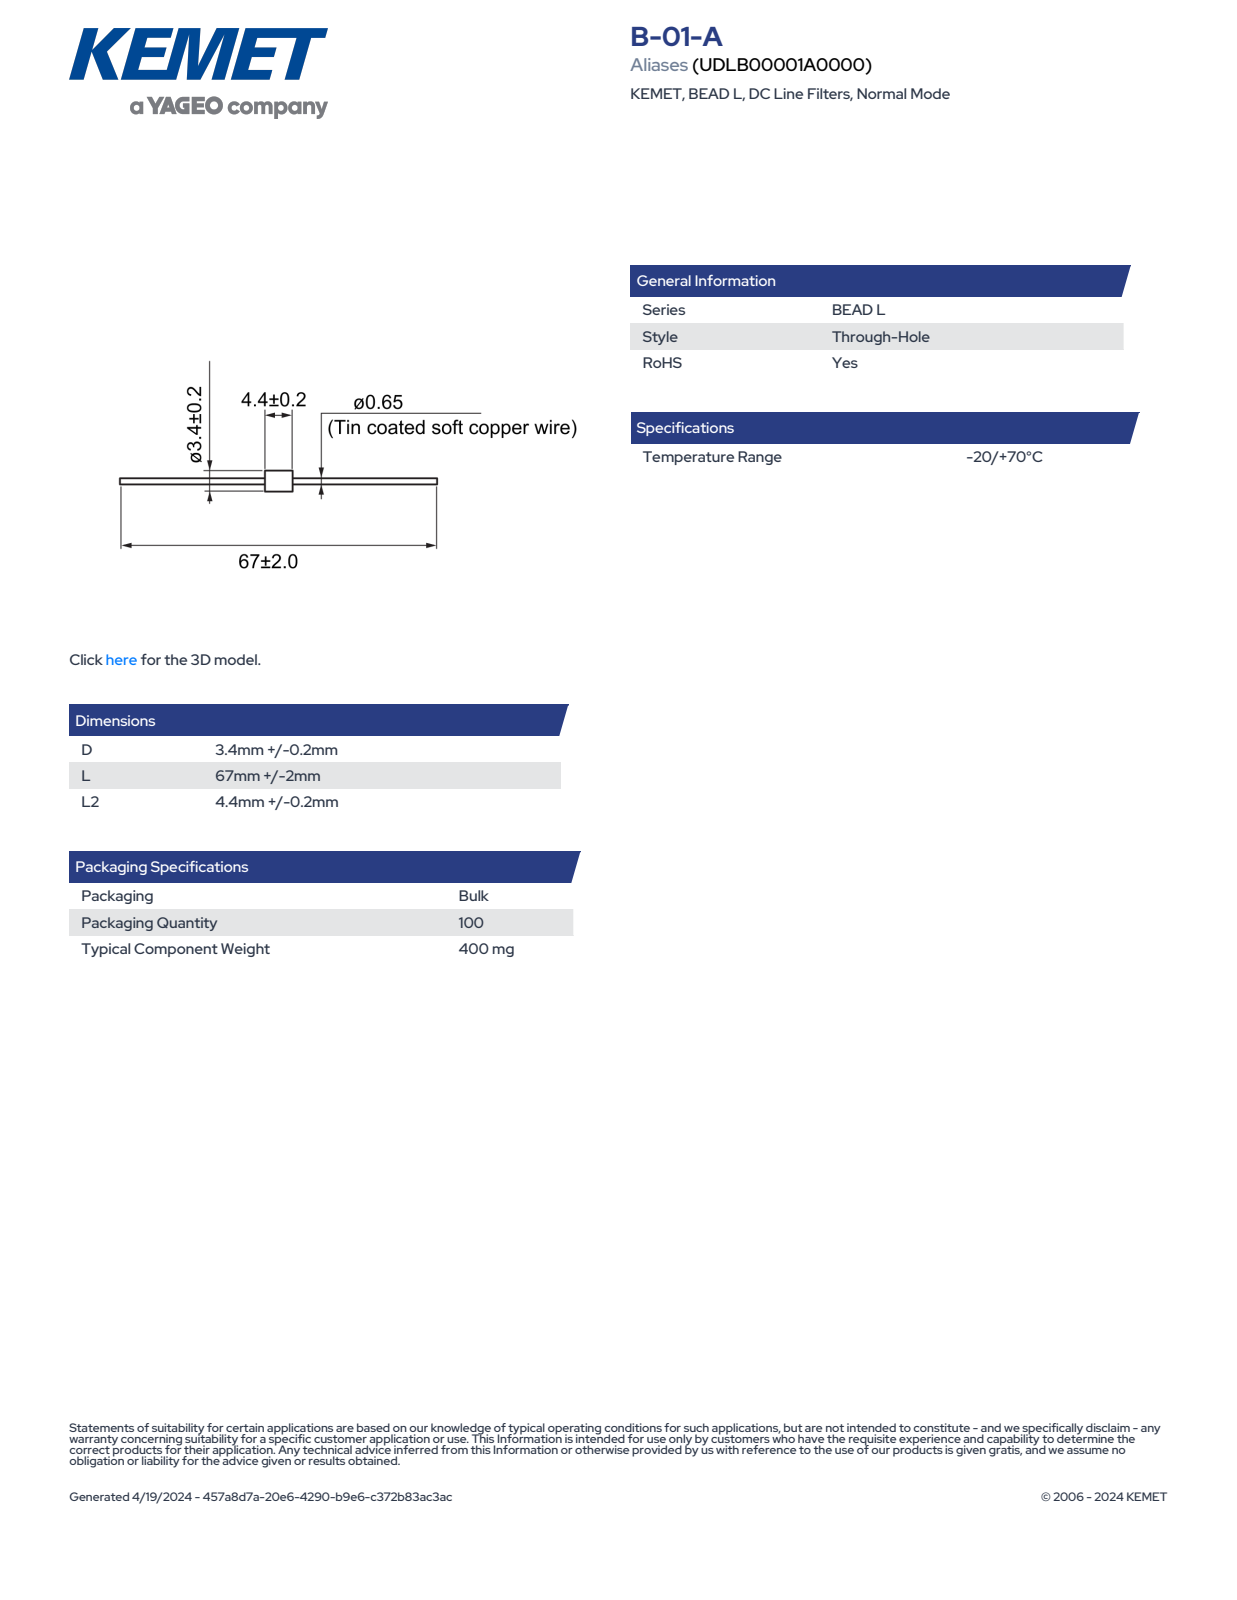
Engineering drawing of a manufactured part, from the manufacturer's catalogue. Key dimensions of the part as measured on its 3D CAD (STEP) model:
Part name (STEP PRODUCT): Default
STEP written by: SolidWorks 2014 (AUTOMOTIVE_DESIGN)
Units: millimetres
Bodies: 1 solid, 72 faces (26 planar, 15 cylindrical, 31 other)
Overall size (bounding box): 69 × 3.61 × 3.6
Volume: 68 mm³ · Surface area: 204 mm²
Round bosses / shafts (diameter × count): ⌀3.6 ×1, ⌀0.65 ×1
Partial cylindrical surfaces — rounded edges, fillets, slot ends (radius × count): R1.81 ×1
Main face-to-face distances: 4.6, 32.2, 36.8, 69
